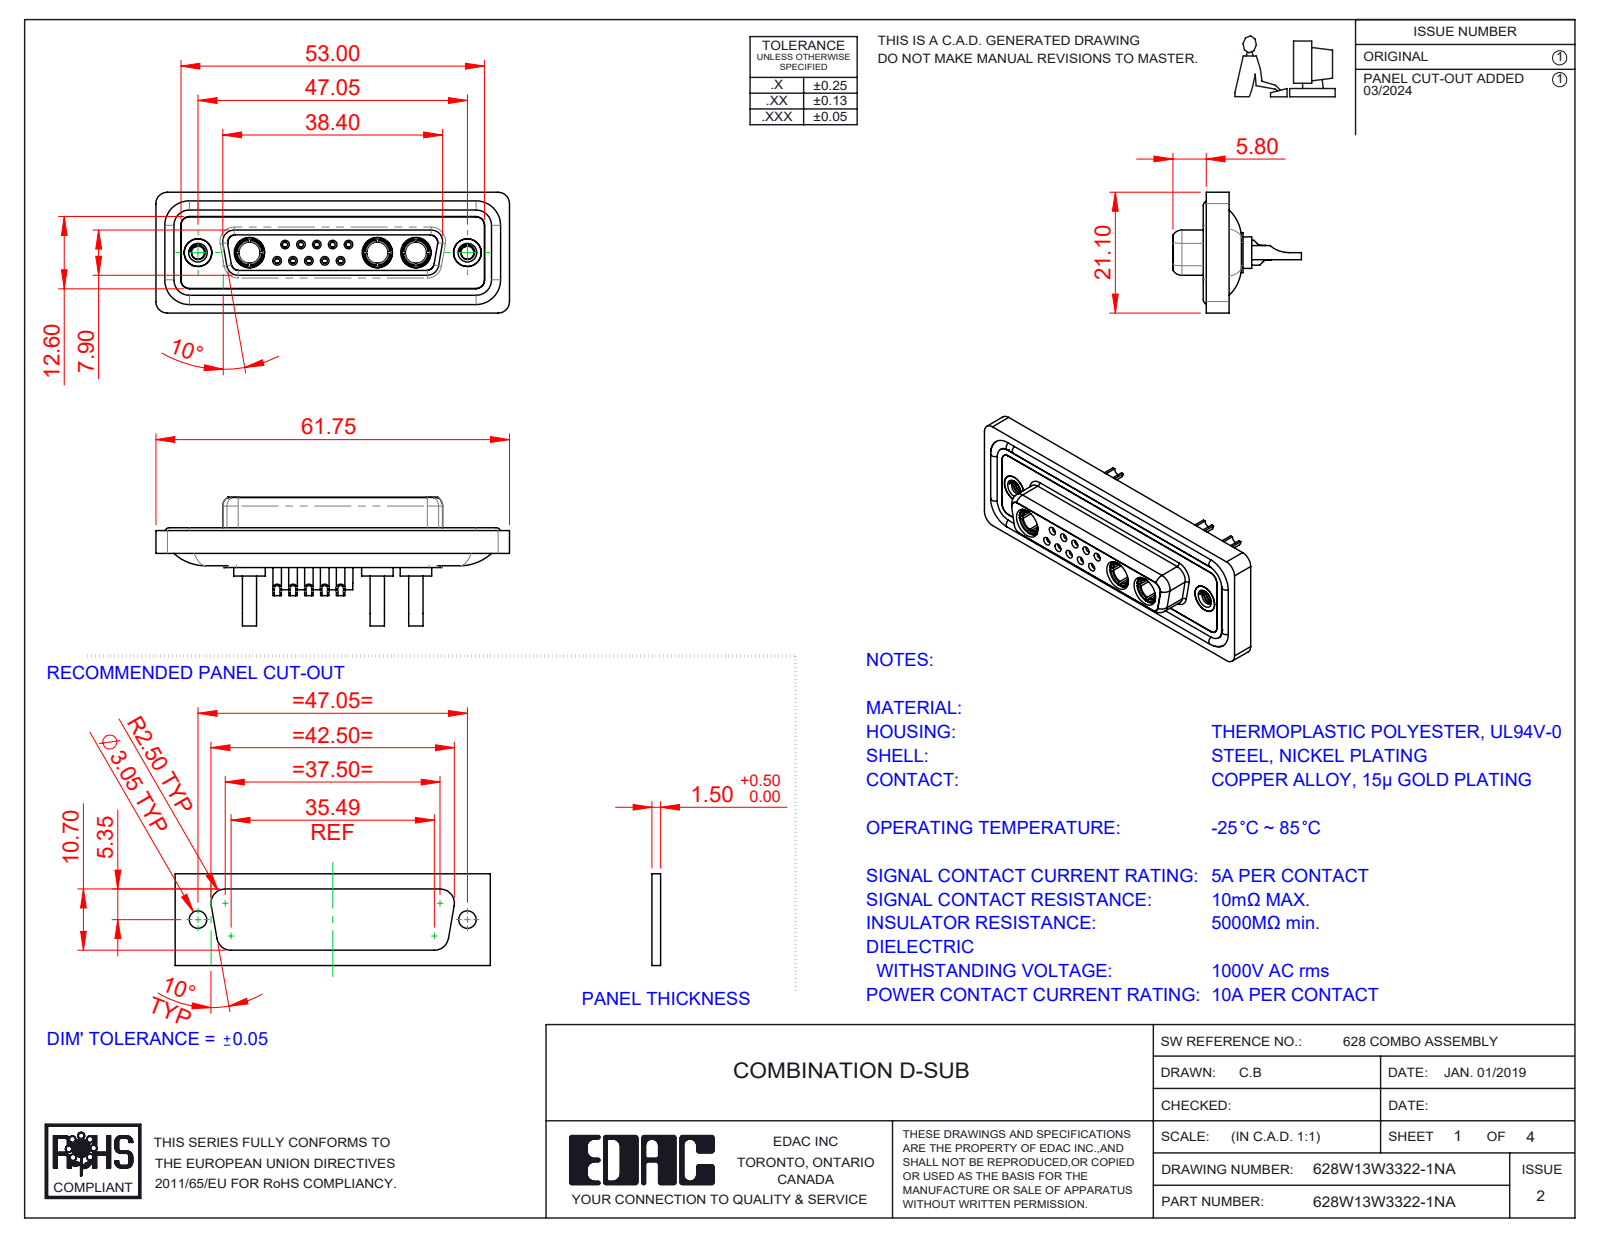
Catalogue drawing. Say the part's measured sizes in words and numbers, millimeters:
The part is named "628Combo Contact Row 1_22; 628Combo Housing_13W3; 628Combo Waterproof Housing_25 Contacts; 628Combo Contact Row 2_22 (+5 more)". Its 3-D file was written by "SolidWorks 2023 (CONFIG_CONTROL_DESIGN)". It is 23 solids with 1171 faces: 368 planar, 478 cylindrical and 325 other. Overall it measures 61.75 by 22.45 by 21.1 millimeters. Its volume is 8 287 cubic millimeters and its surface area 13 954 square millimeters. Round holes: 10 of diameter 0.9, 10 of diameter 1, 10 of diameter 1.1, 10 of diameter 1.5, 10 of diameter 2, 5 of diameter 1.6, 5 of diameter 1.7, 5 of diameter 4.85, 3 of diameter 1.7, 3 of diameter 3.7, 3 of diameter 5.3, 2 of diameter 2.26. Round bosses or shafts: 10 of diameter 2.2, 9 of diameter 1.6, 3 of diameter 5.5, 3 of diameter 5.2, 3 of diameter 4.96, 3 of diameter 4.75, 3 of diameter 3.75, 3 of diameter 2.5. Partial cylindrical surfaces (rounded edges, fillets, slot ends): 22 of radius 1.5, 18 of radius 2, 8 of radius 1.35, 8 of radius 1.6, 6 of radius 1, 4 of radius 0.25, 4 of radius 0.5, 4 of radius 0.6. The main face-to-face distances are 0.4, 1.8, 7.45, 5.65, 0.5, 6.6, 7.05, 1.6, 2.9, 1.1. The hole center spacings are 3.16, 2.77, 5.03, 5.04, 5.54, 8.31, 7.49, 2.76.
